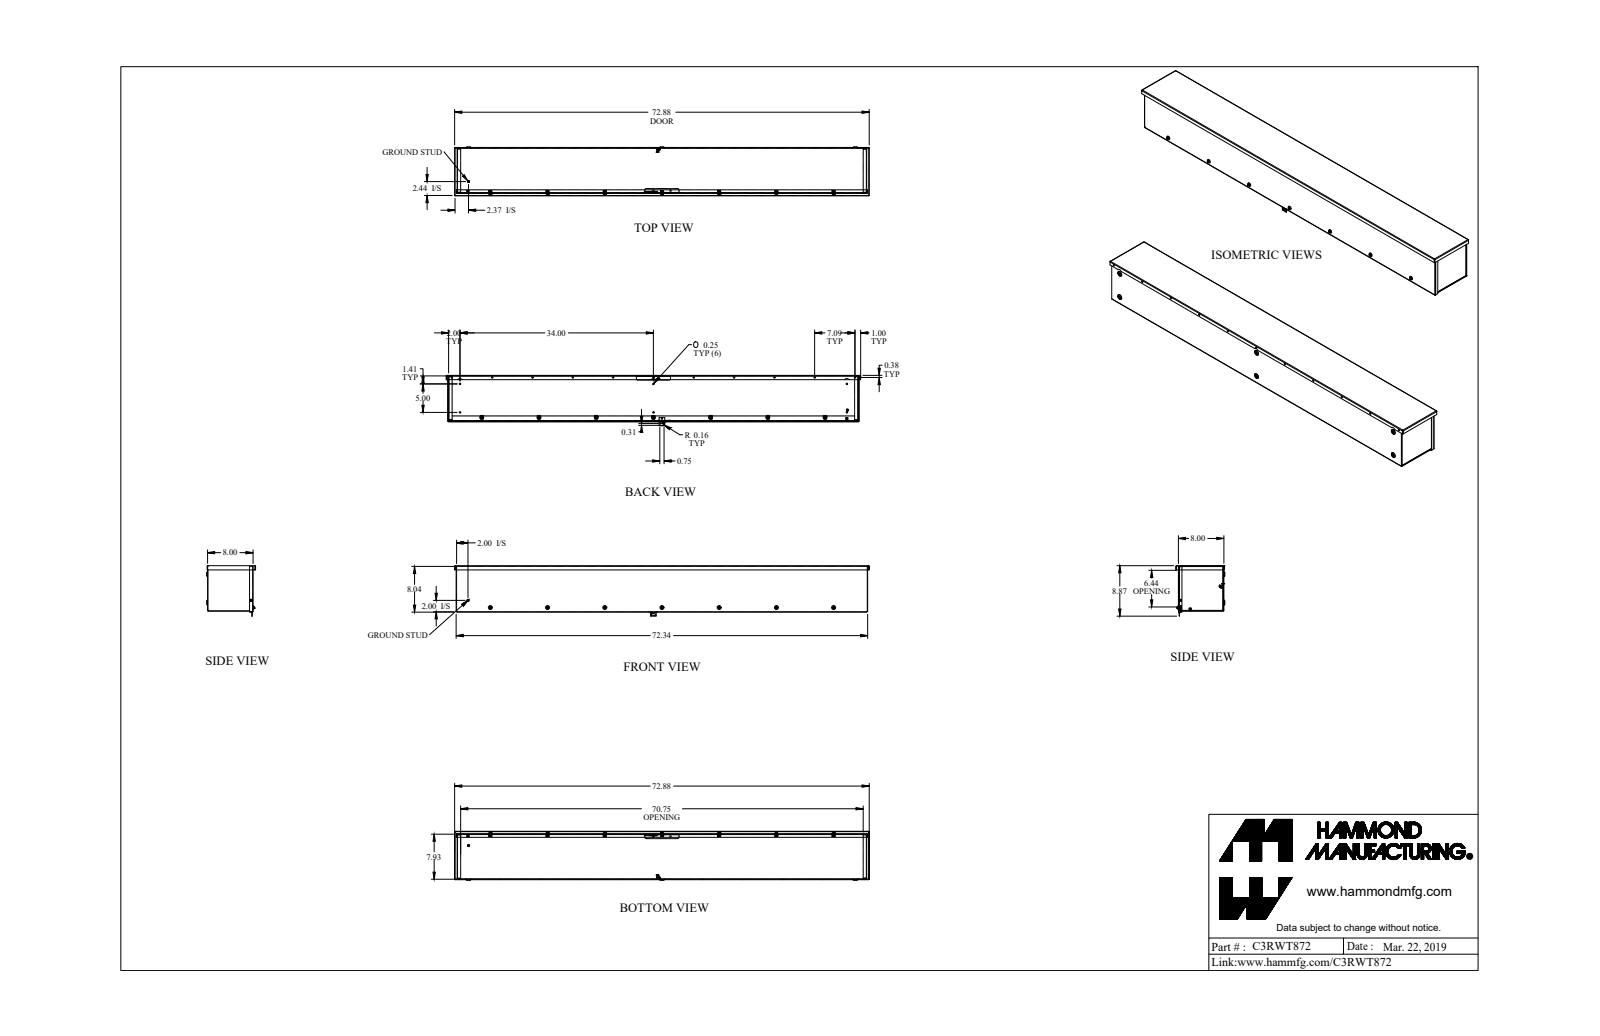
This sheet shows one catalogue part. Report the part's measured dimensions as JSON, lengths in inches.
{"part_name": "C3RWT872_Default", "step_written_by": "SolidWorks 2019 (CONFIG_CONTROL_DESIGN)", "units": "inches", "bodies": {"solids": 35, "faces": 1321, "planar": 712, "cylindrical": 421, "other": 188}, "overall_size": [72.875, 8.871, 8.594], "volume_in3": 195.4, "surface_area_in2": 5487, "round_holes": [[0.25, 19], [0.156, 9], [0.214, 7], [0.23, 7], [0.203, 2], [0.125, 1], [0.137, 1], [0.2, 1], [0.215, 1]], "round_bosses_or_shafts": [[0.19, 8], [0.148, 7], [0.375, 2], [0.5, 1], [0.367, 1], [0.21, 1], [0.152, 1], [0.125, 1]], "partial_cylinders_radius": [[0.08, 28], [0.108, 28], [0.036, 18], [0.108, 18], [0.125, 15], [0.022, 14], [0.171, 7], [0.206, 7]], "face_to_face_distances": [0.072, 7.928, 8, 0.072, 7.856, 7.856, 7.928, 0.144, 71.928, 8.366], "hole_center_spacings": [7.087, 21.263, 28.35, 14.175, 10.057, 14.175, 20.115, 30.172]}
